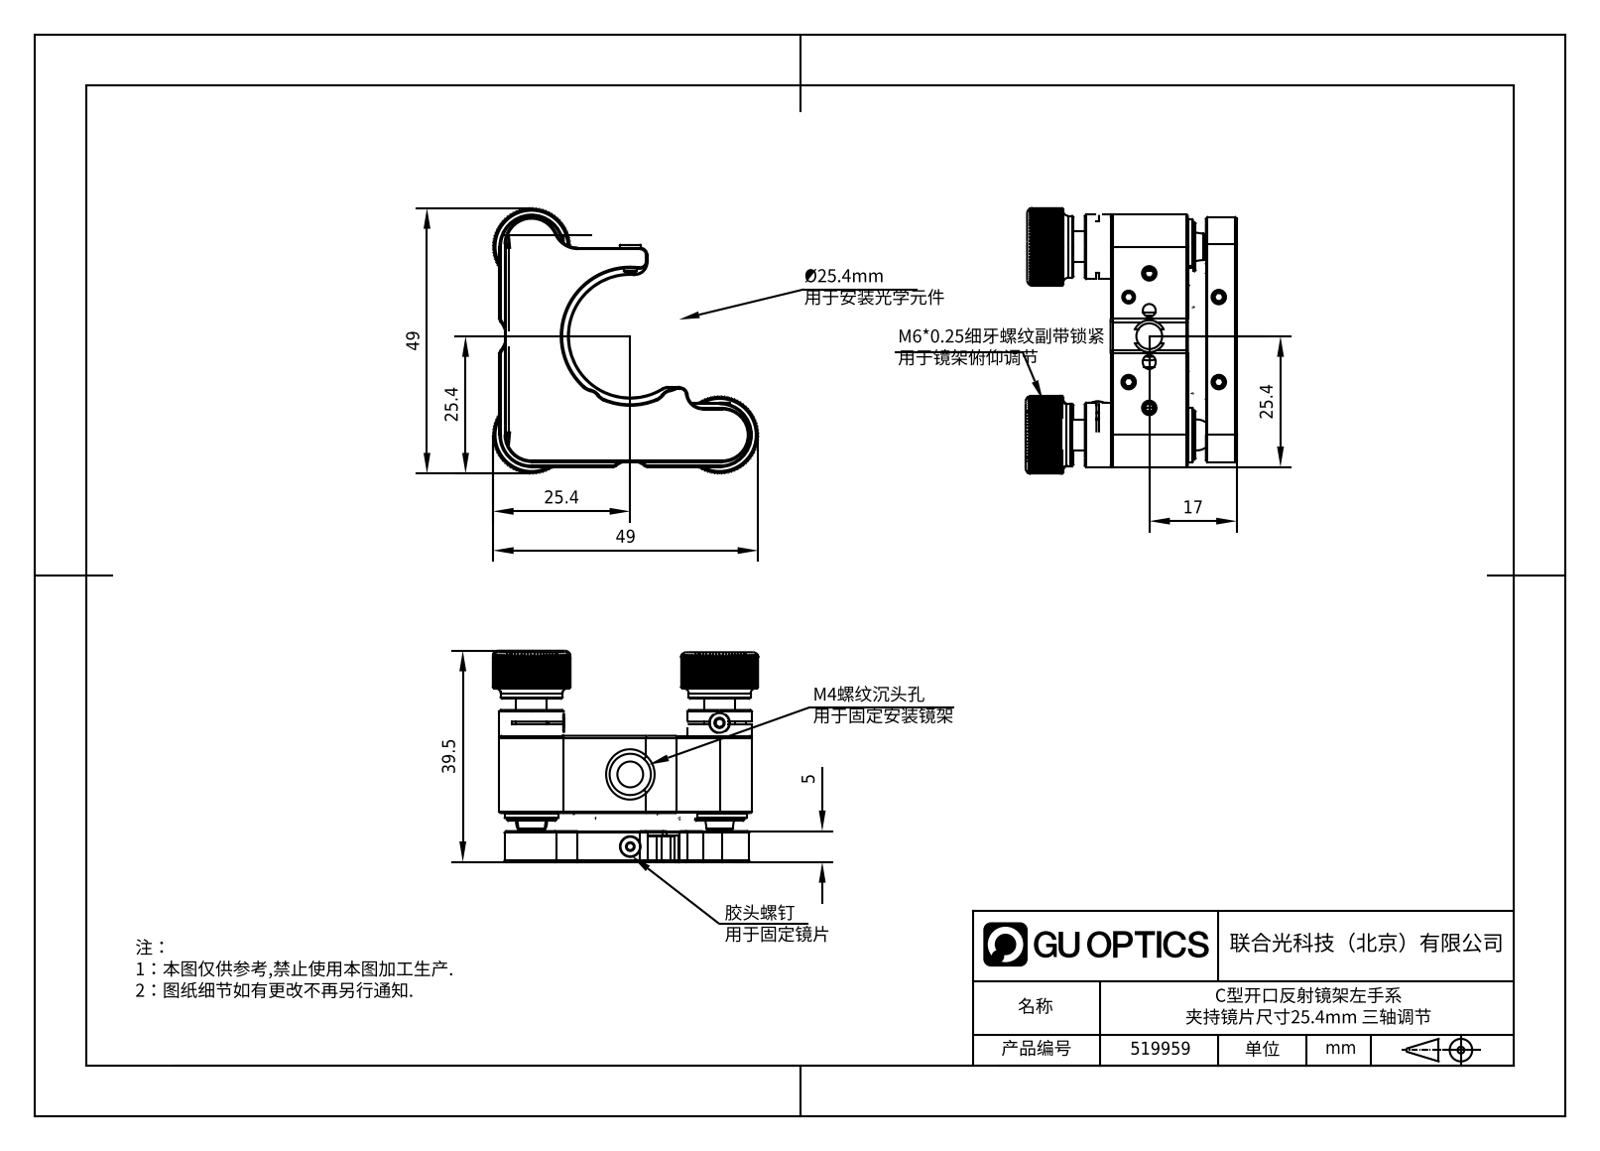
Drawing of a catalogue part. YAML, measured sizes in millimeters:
part_name: "JC版，2.1.13.6，OMC-1.0L-3，1英寸C型开口反射调整架，左手，3轴"
step_written_by: "SolidWorks 2023 (AUTOMOTIVE_DESIGN)"
units: millimeters
bodies: {solids: 0, faces: 1308, planar: 627, cylindrical: 413, other: 268}
overall_size: [51.5, 51.5, 41]
round_holes:
  - {diameter: 6, count: 4}
  - {diameter: 2.5, count: 3}
  - {diameter: 4, count: 3}
  - {diameter: 4.6, count: 2}
  - {diameter: 5, count: 2}
  - {diameter: 8, count: 2}
  - {diameter: 3.3, count: 1}
round_bosses_or_shafts:
  - {diameter: 3, count: 8}
  - {diameter: 4, count: 4}
  - {diameter: 1.5, count: 4}
  - {diameter: 12.5, count: 3}
  - {diameter: 12, count: 3}
  - {diameter: 9.5, count: 3}
  - {diameter: 6, count: 3}
  - {diameter: 10.5, count: 2}
partial_cylinders:
  - {radius: 0.8, count: 8}
  - {radius: 2.5, count: 7}
  - {radius: 0.3, count: 6}
  - {radius: 1.5, count: 5}
  - {radius: 0.5, count: 4}
  - {radius: 1, count: 4}
  - {radius: 1.25, count: 4}
  - {radius: 5.25, count: 3}
face_to_face_distances: [6, 24.5, 18.5, 3.5, 9.5, 15, 1, 2.25, 2.75, 11.5]
hole_center_spacings: [5, 9.75, 10.25, 16.5, 26.25, 26.75, 28.65, 36.5]
